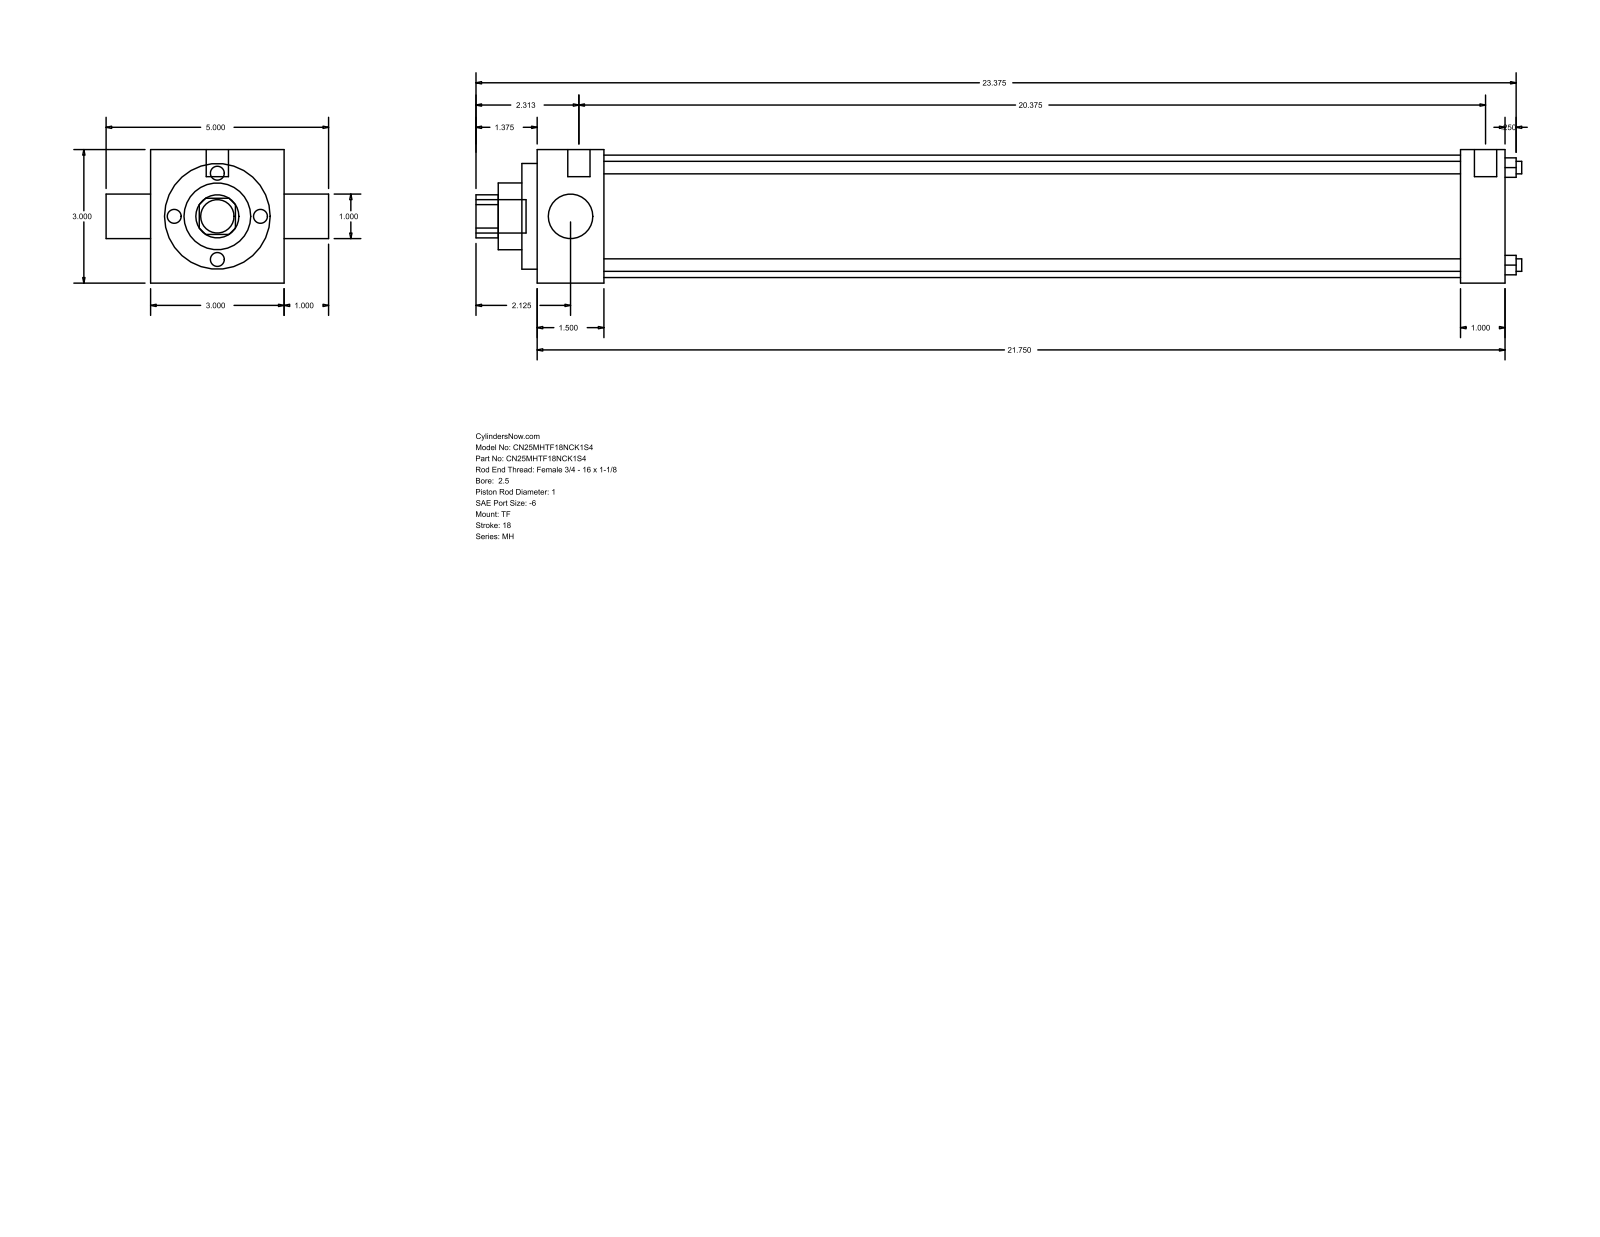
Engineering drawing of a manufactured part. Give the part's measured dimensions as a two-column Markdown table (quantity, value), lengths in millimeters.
| quantity | value |
| --- | --- |
| part name | MH_TF__0250_1 |
| STEP written by | GSSL Pune (CONFIG_CONTROL_DESIGN) |
| units | millimeters |
| bodies | 0 solids, 86 faces (61 planar, 25 cylindrical, 0 other) |
| overall size | 596.9 × 127 × 76.2 |
| round holes (diameter × count) | 7.14 × 4, 25.4 × 2, 38.1 × 1, 60.33 × 1, 69.85 × 1 |
| round bosses / shafts (diameter × count) | 5.56 × 3, 12.7 × 2, 19.05 × 1 |
| partial cylindrical surfaces (radius × count) | 12.29 × 1 |
| main face-to-face distances | 76.2, 552.46, 25.4, 38.11, 514.35, 527.06, 488.95, 8.73, 46.84, 535.79 |
| hole center spacings | 39.33, 55.62, 78.66 |
